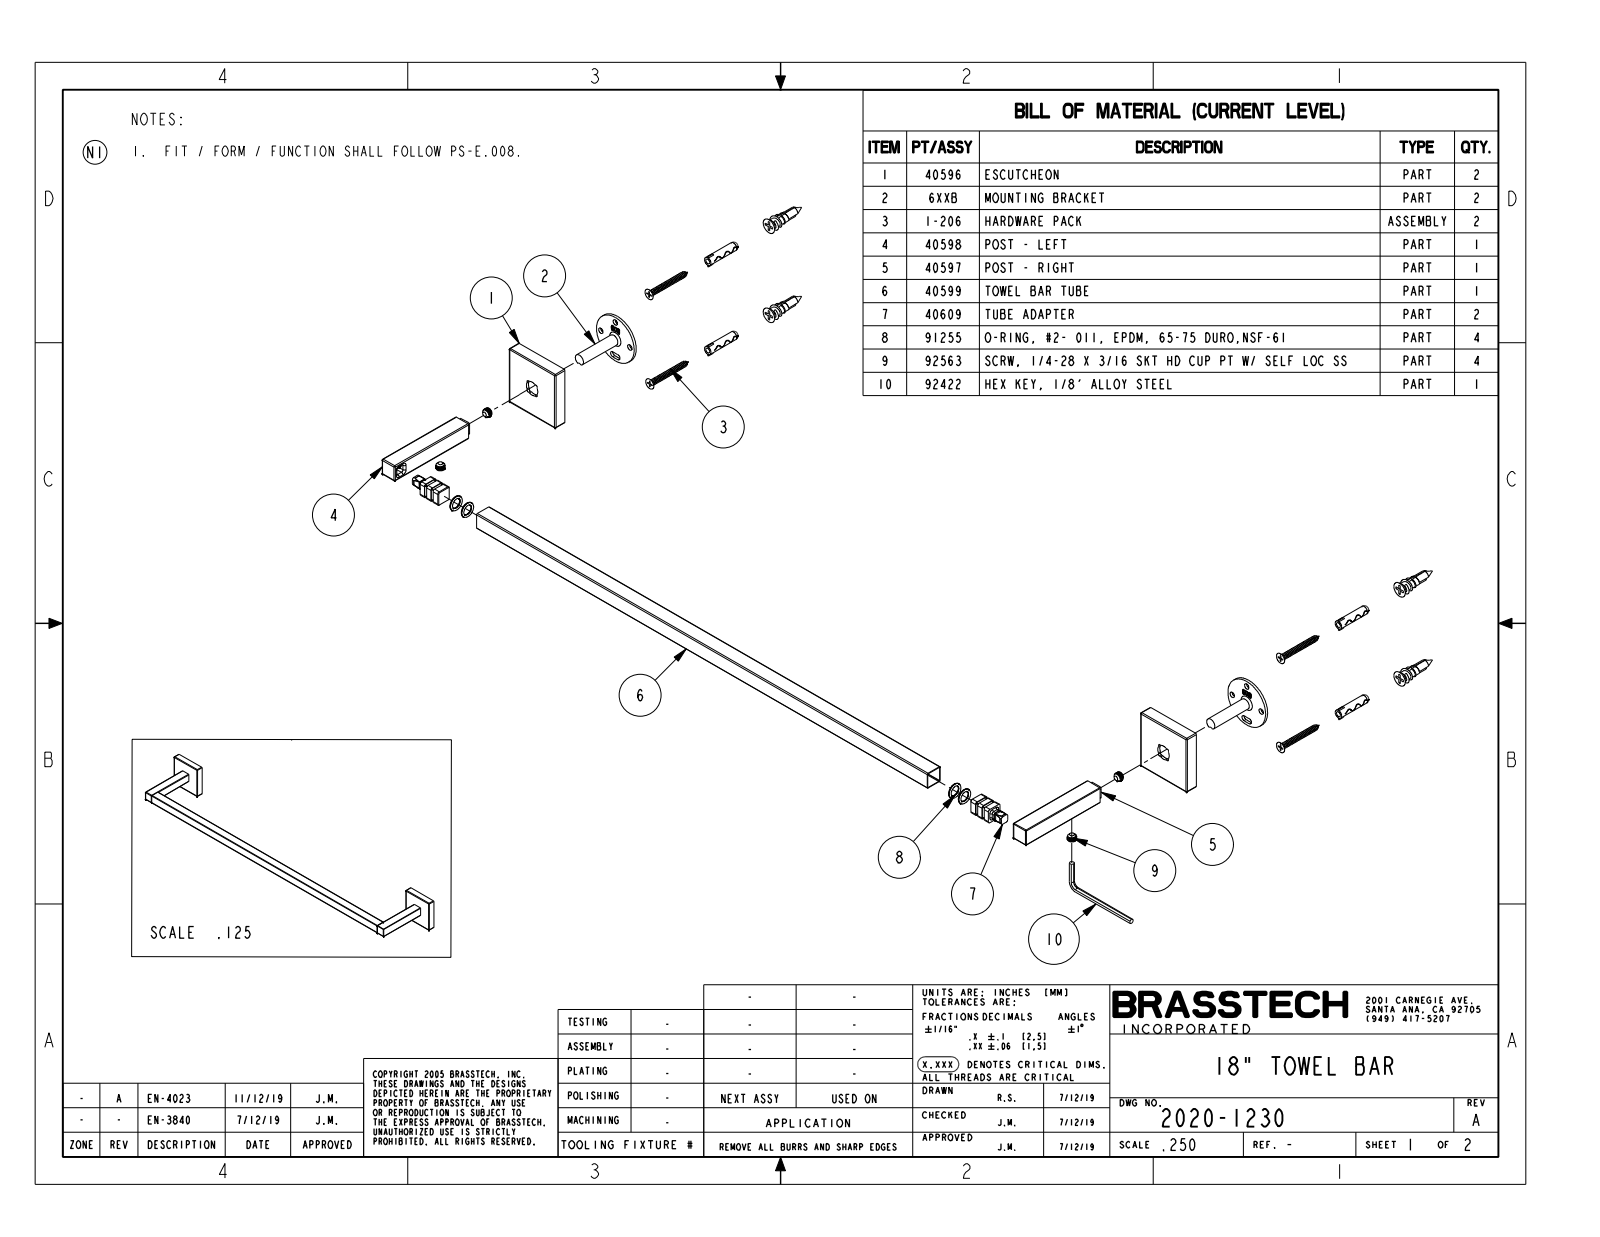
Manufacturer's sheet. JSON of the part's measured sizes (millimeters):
{"part_name": "40596; 6XXB; 40598; 40597 (+5 more)", "step_written_by": "CREO PARAMETRIC BY PTC INC, 2018400 (CONFIG_CONTROL_DESIGN)", "units": "millimeters", "bodies": {"solids": 16, "faces": 1151, "planar": 455, "cylindrical": 369, "other": 327}, "overall_size": [502.9, 82.6, 45.7], "volume_mm3": 49360, "surface_area_mm2": 114600, "round_holes": [[4.3, 3], [5.4, 2], [5.5, 2], [8.2, 2], [7.6, 1]], "round_bosses_or_shafts": [[6.4, 4], [37.1, 1], [11.5, 1], [8, 1]], "partial_cylinders_radius": [[0.8, 46], [0.3, 32], [1.5, 24], [1.1, 16], [1.3, 16], [0.5, 8], [1.2, 8], [2.2, 2]], "face_to_face_distances": [12.7, 0.5, 12.2, 11.7, 60.3, 73, 16.5, 29.2, 457.2, 2], "hole_center_spacings": [457.2, 14.3, 0.8, 14.3, 20.2, 442.9, 471.5, 15.1]}
